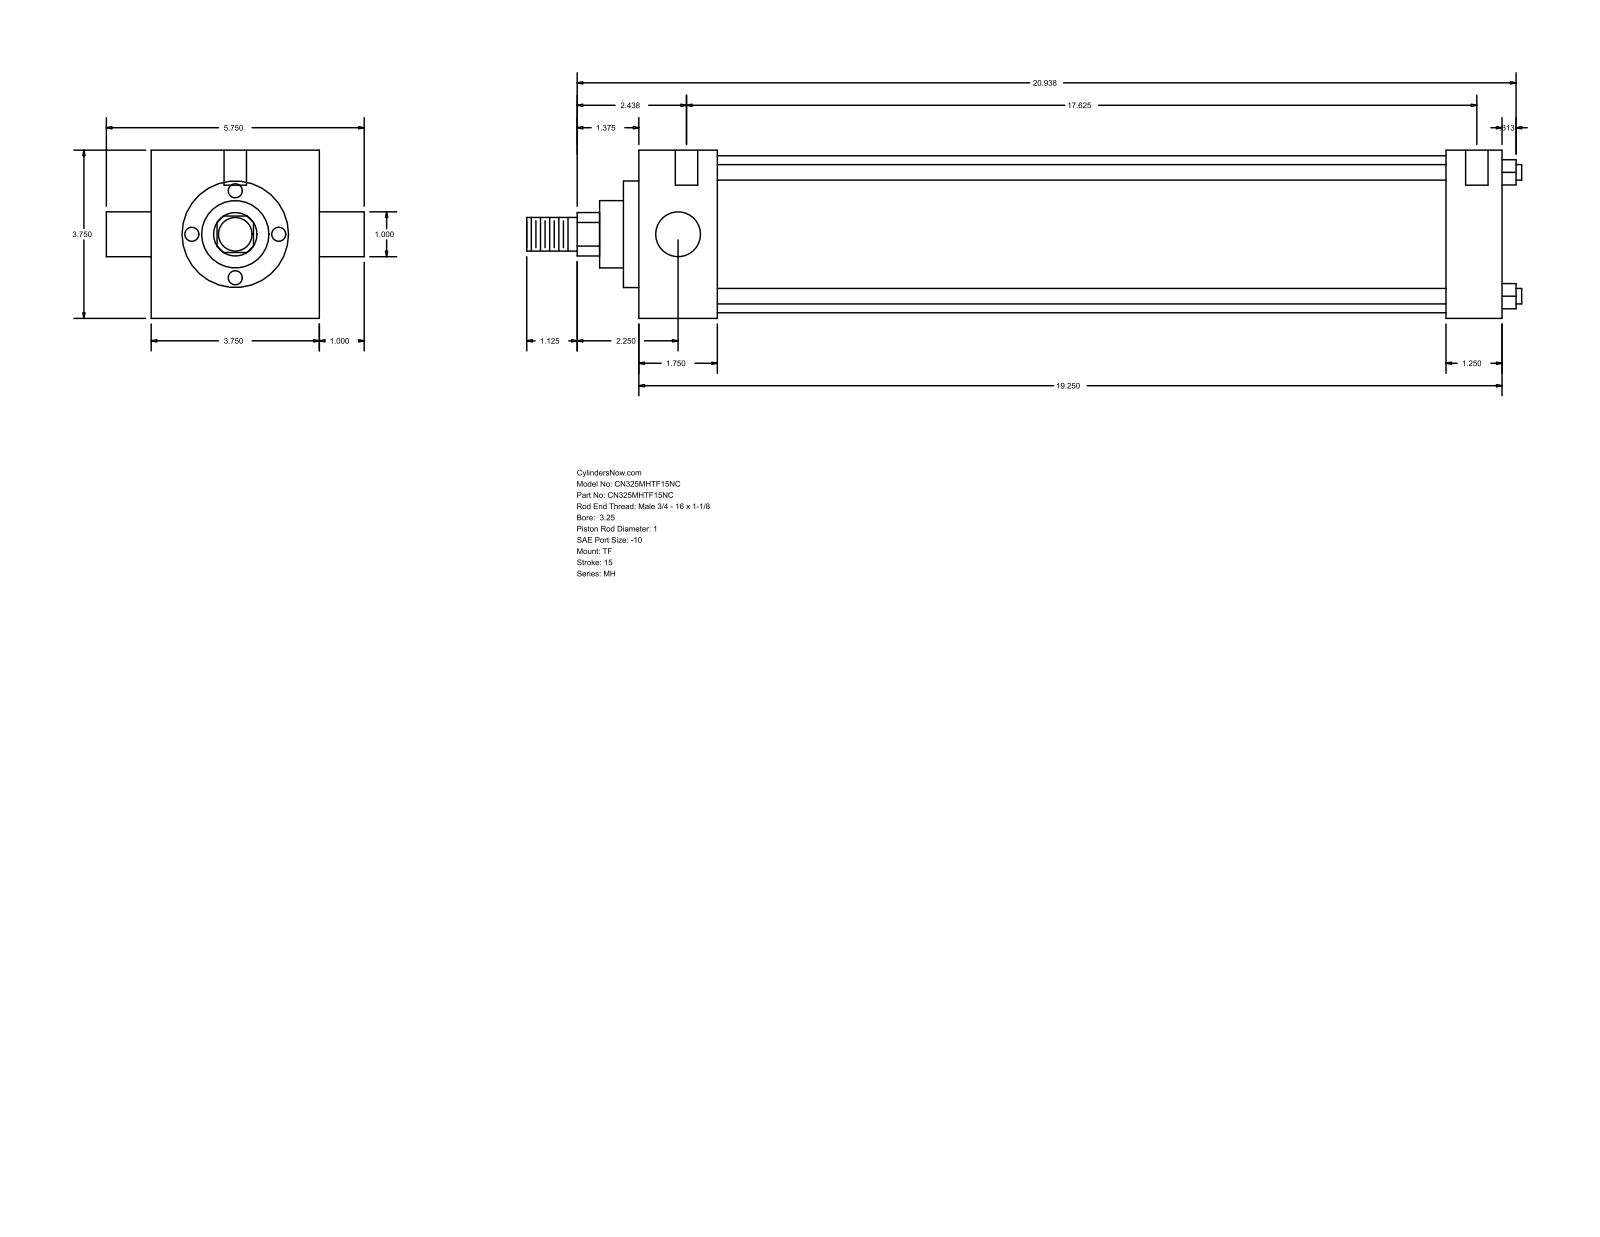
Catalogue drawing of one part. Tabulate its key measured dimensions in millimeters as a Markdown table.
| quantity | value |
| --- | --- |
| part name | MH_TF__0325_1 |
| STEP written by | GSSL Pune (CONFIG_CONTROL_DESIGN) |
| units | millimeters |
| bodies | 0 solids, 86 faces (61 planar, 25 cylindrical, 0 other) |
| overall size | 563.56 × 146.05 × 95.25 |
| round holes (diameter × count) | 5.56 × 3, 12.7 × 2 |
| round bosses / shafts (diameter × count) | 8.76 × 4, 25.4 × 2, 88.9 × 1, 60.33 × 1, 38.1 × 1, 19.05 × 1 |
| partial cylindrical surfaces (radius × count) | 12.29 × 1 |
| main face-to-face distances | 95.24, 488.96, 44.46, 457.2, 412.74, 444.5, 31.76, 8.73, 53.19, 465.93 |
| hole center spacings | 1.58, 4.76, 447.68, 449.26, 452.44, 454.02 |
